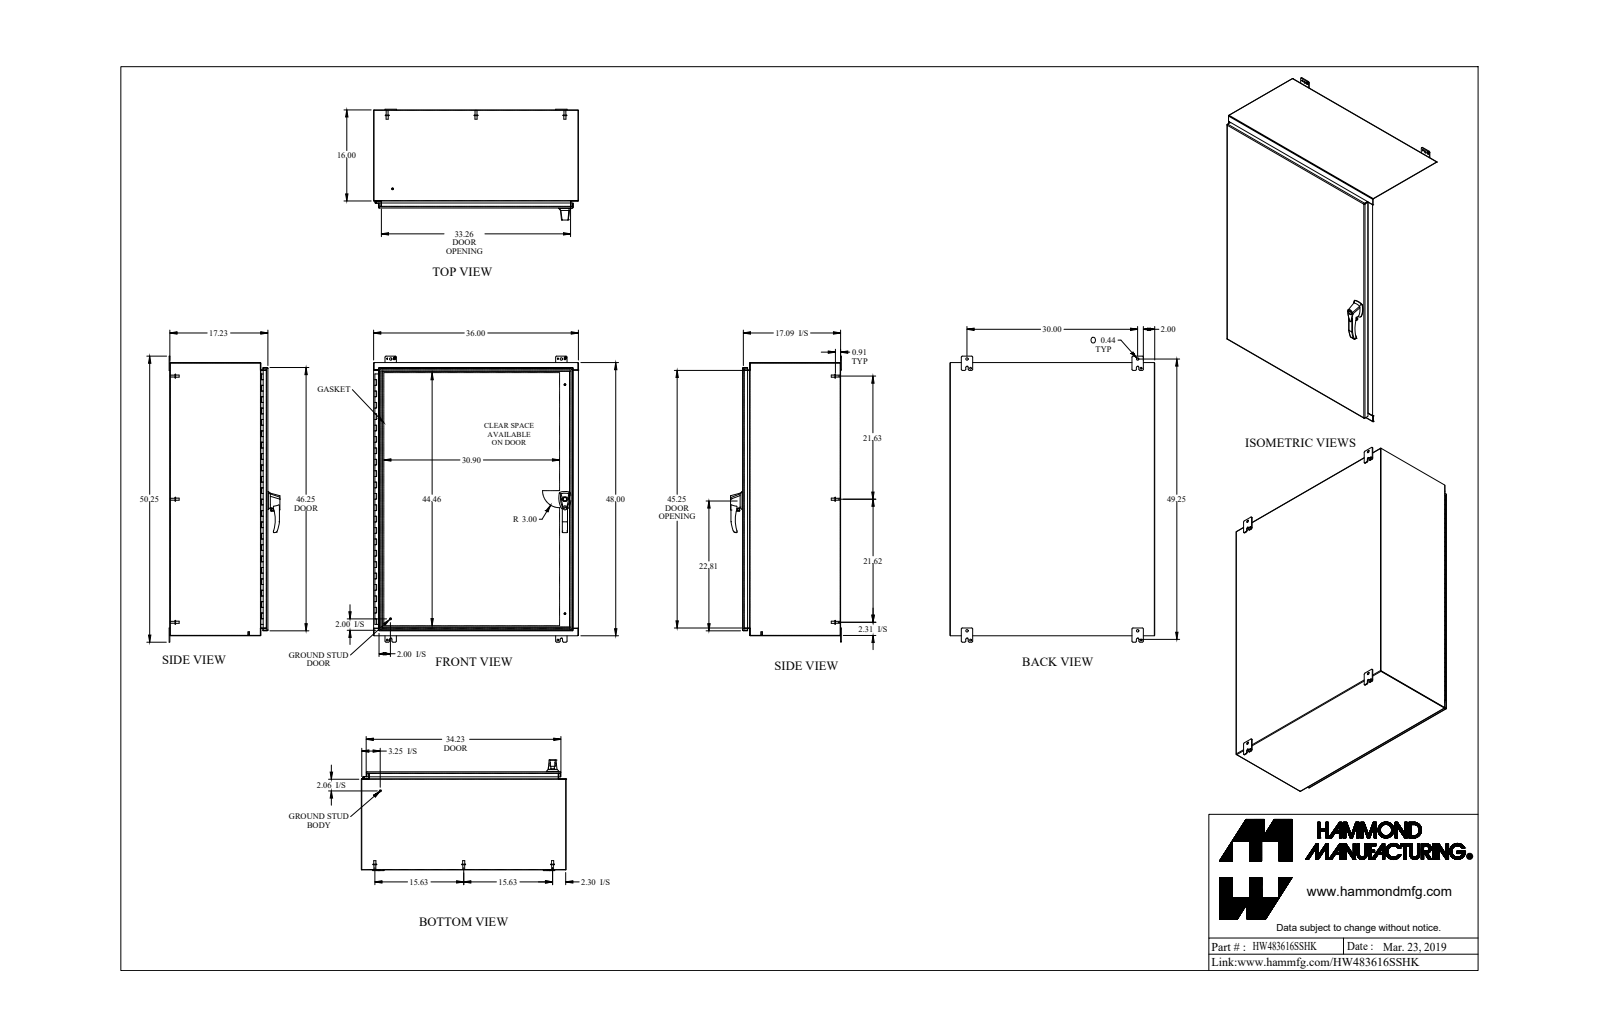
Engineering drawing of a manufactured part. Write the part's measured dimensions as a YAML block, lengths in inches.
part_name: "HW483616SSHK"
step_written_by: "SolidWorks 2018 (AUTOMOTIVE_DESIGN)"
units: inches
bodies: {solids: 48, faces: 1592, planar: 761, cylindrical: 693, other: 138}
overall_size: [50.25, 36, 19.473]
volume: 556.4
surface_area: 13938
round_holes:
  - {diameter: 0.176, count: 6}
  - {diameter: 0.313, count: 5}
  - {diameter: 0.25, count: 3}
  - {diameter: 0.265, count: 3}
  - {diameter: 0.413, count: 3}
  - {diameter: 0.196, count: 2}
  - {diameter: 0.256, count: 2}
  - {diameter: 0.394, count: 2}
  - {diameter: 0.437, count: 2}
  - {diameter: 0.187, count: 1}
  - {diameter: 0.233, count: 1}
  - {diameter: 0.33, count: 1}
round_bosses_or_shafts:
  - {diameter: 0.375, count: 13}
  - {diameter: 0.65, count: 8}
  - {diameter: 0.332, count: 8}
  - {diameter: 0.25, count: 7}
  - {diameter: 0.156, count: 6}
  - {diameter: 1, count: 3}
  - {diameter: 0.51, count: 3}
  - {diameter: 0.63, count: 2}
partial_cylinders:
  - {radius: 0.25, count: 27}
  - {radius: 0.188, count: 20}
  - {radius: 0.036, count: 14}
  - {radius: 0.108, count: 14}
  - {radius: 0.06, count: 12}
  - {radius: 0.125, count: 9}
  - {radius: 0.218, count: 8}
  - {radius: 0.03, count: 6}
face_to_face_distances: [0.072, 17.138, 17.066, 0.095, 17.233, 17.161, 35.928, 47.928, 35.856, 36]
hole_center_spacings: [1.111, 20.118, 20.119, 40.237, 20.119, 30, 30.665, 38.744]
